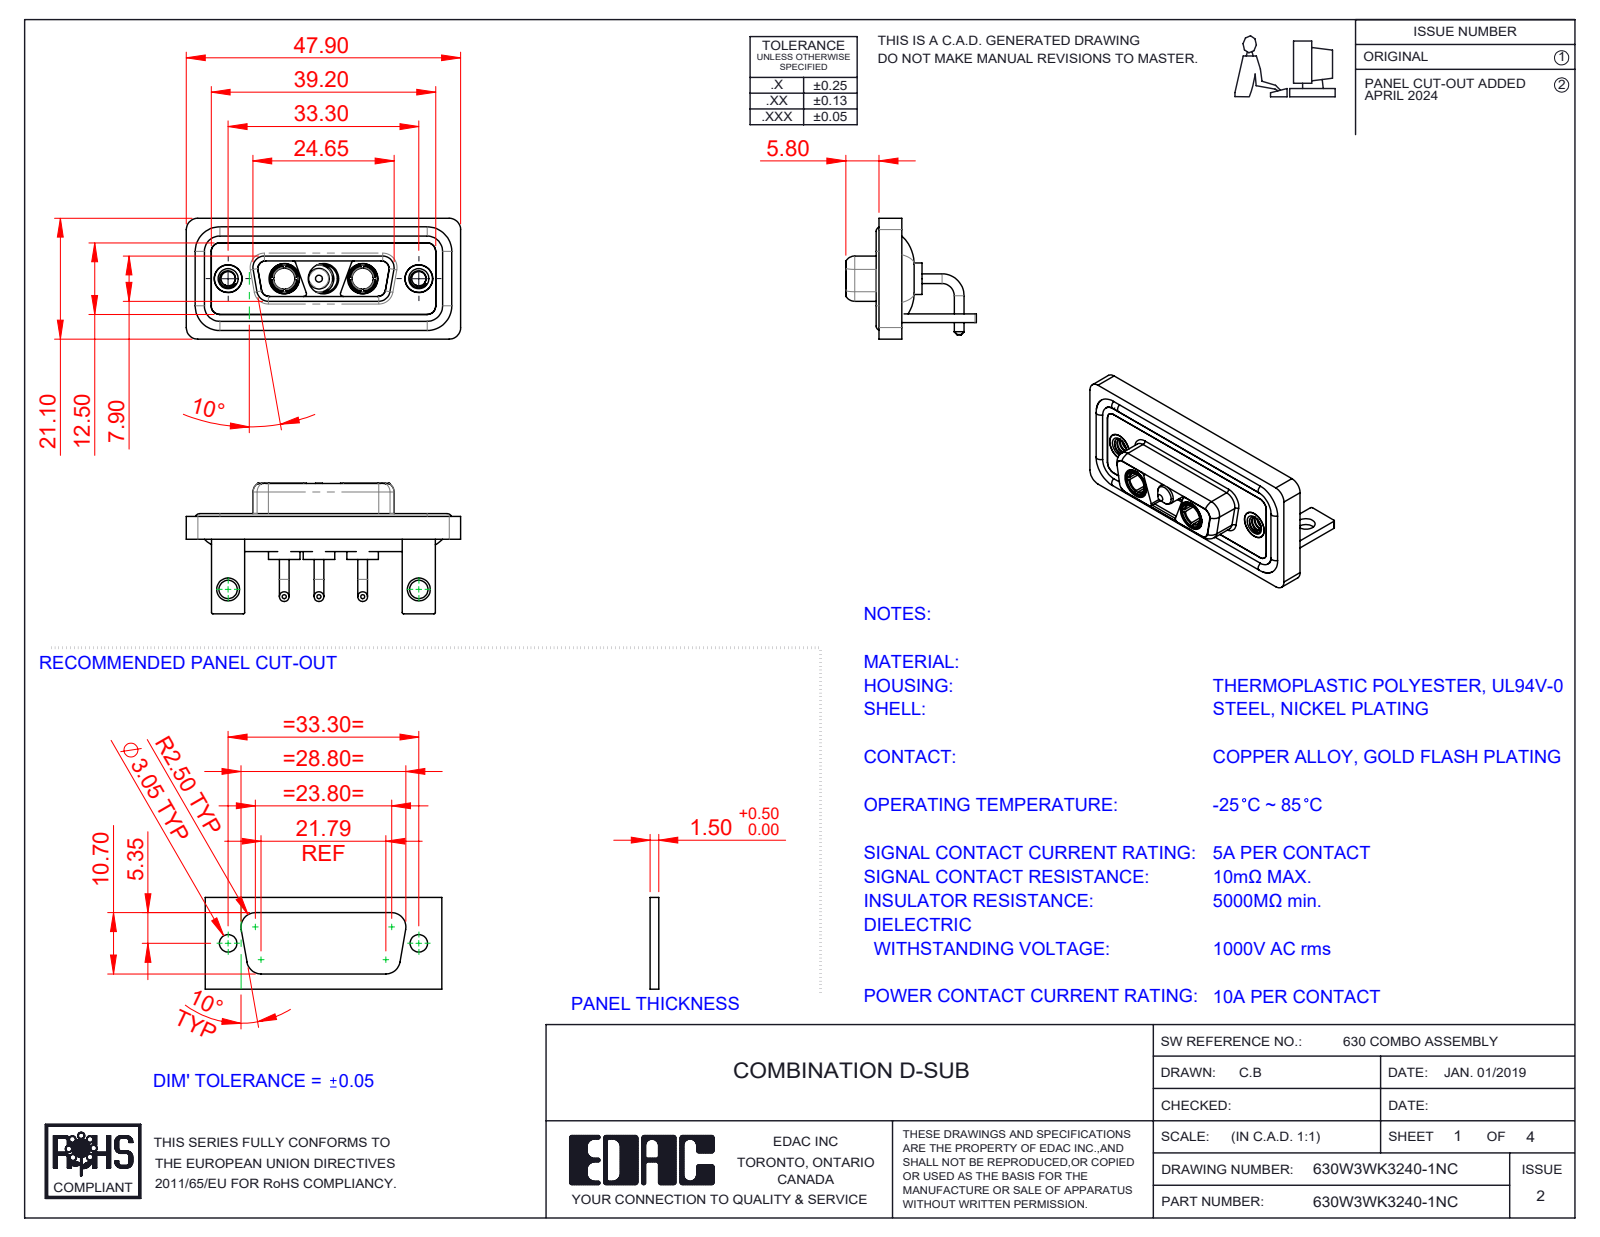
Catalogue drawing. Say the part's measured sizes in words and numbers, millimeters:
The part is named "630Combo Stabilizer Bracket_50 Contacts; Power Socket_10A RA; 630W3WK3140-1NC; 630Combo Waterproof Housing_15 Contacts (+5 more)". Its 3-D file was written by "SolidWorks 2023 (CONFIG_CONTROL_DESIGN)". It is 15 solids with 637 faces: 198 planar, 286 cylindrical and 153 other. Overall it measures 47.9 by 22.8 by 21.1 millimeters. Its volume is 6 218 cubic millimeters and its surface area 10 325 square millimeters. Round holes: 5 of diameter 4.85, 3 of diameter 5.3, 2 of diameter 2.5, 2 of diameter 3.2, 2 of diameter 3.7, 2 of diameter 4, 2 of diameter 4.05, 2 of diameter 5. Round bosses or shafts: 6 of diameter 1.7, 4 of diameter 1.6, 3 of diameter 5.5, 3 of diameter 5.2, 3 of diameter 4.75, 3 of diameter 3.75, 2 of diameter 4.96, 2 of diameter 4.95. Partial cylindrical surfaces (rounded edges, fillets, slot ends): 21 of radius 2, 18 of radius 1.5, 16 of radius 0.25, 12 of radius 1.35, 9 of radius 0.5, 8 of radius 1.6, 4 of radius 0.6, 4 of radius 0.65. The main face-to-face distances are 0.4, 2.9, 1.5, 3.7, 1.8, 1.1, 4.1, 1.6, 2.5, 1.4. The hole center spacings are 6.85, 9.8, 16.65, 23.5, 33.3, 13.7.
